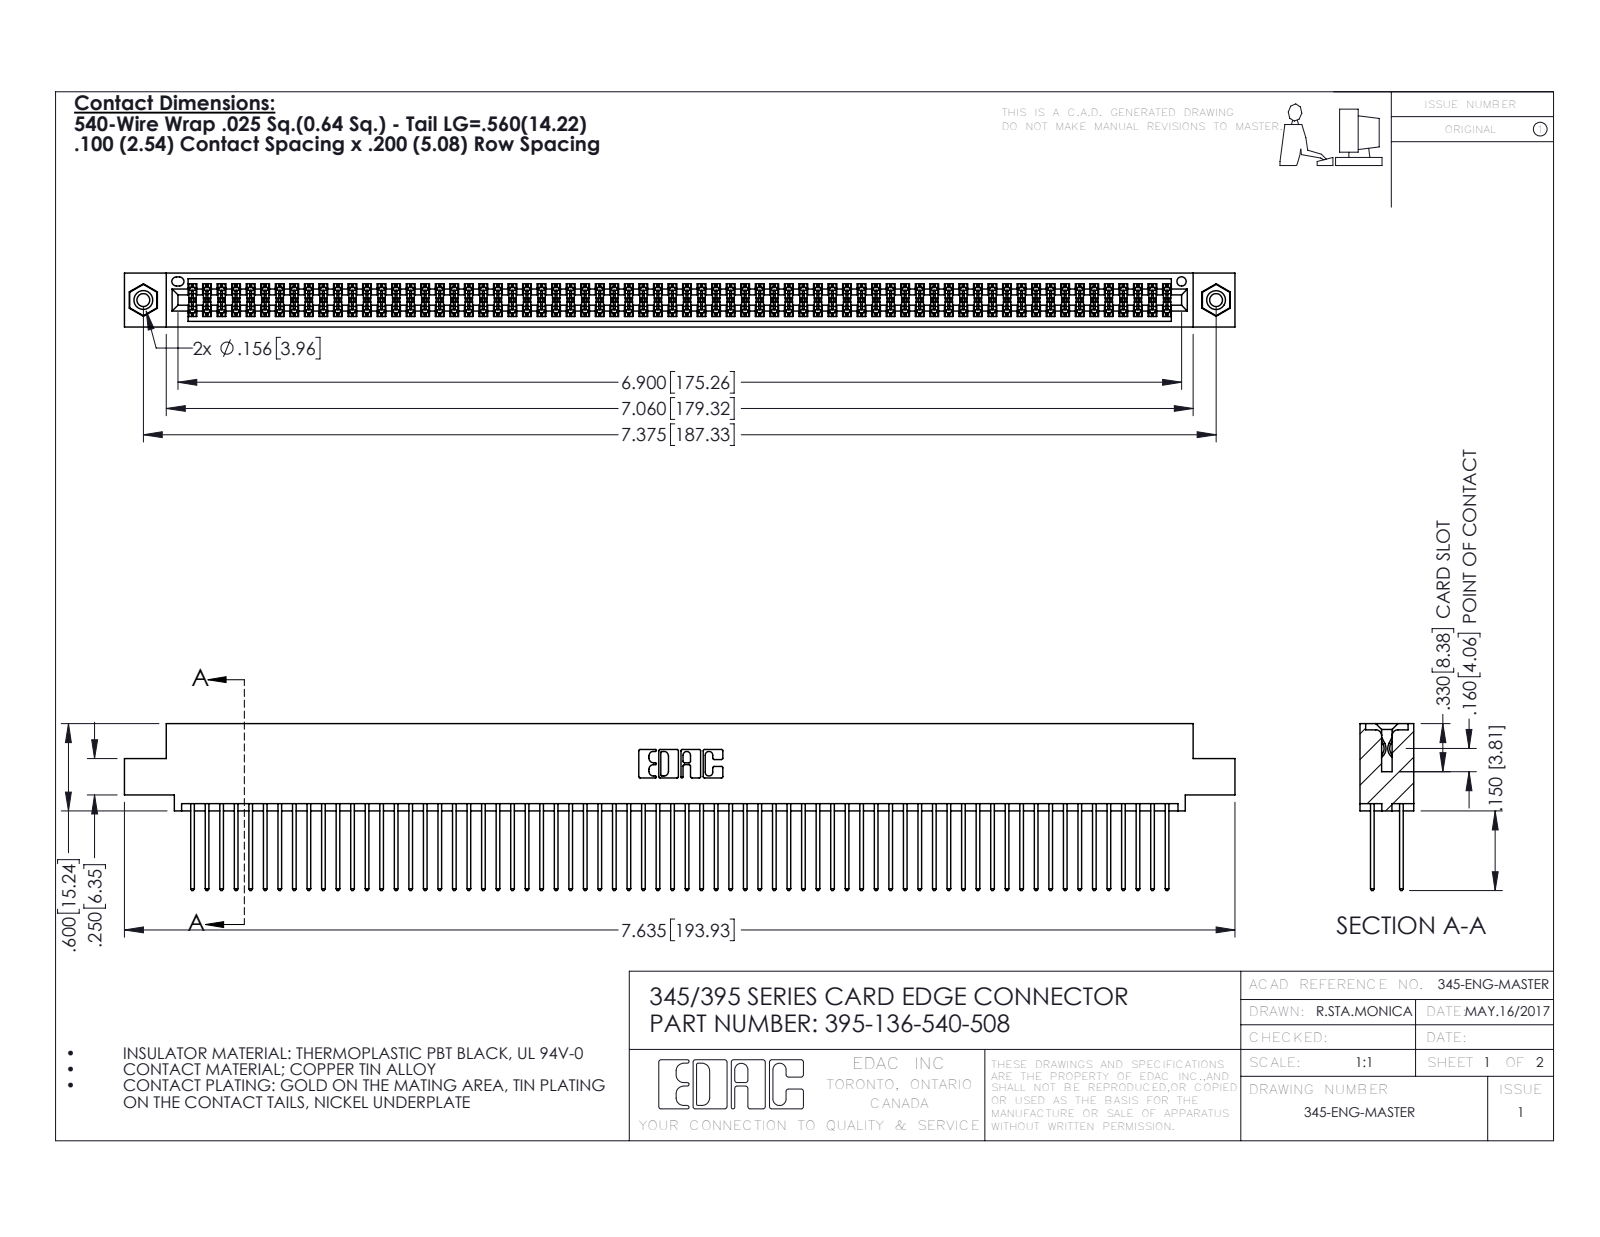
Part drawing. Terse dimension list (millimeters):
name: 345-292-001_345-293-140; 395-136-540-508; 345 Part_0.110 Offset - 0.156 Dia-TI; 345-250-001_345-250-003-102
written by: SolidWorks 2016 (CONFIG_CONTROL_DESIGN)
unit: mm
bodies: 139 solids, 6990 faces (4604 planar, 2370 cylindrical, 16 other)
size: 193.9 × 29.1 × 9.4
volume: 19 520 mm³; area: 31 850 mm²
holes: 2× ⌀2.3, 2× ⌀3.2, 2× ⌀4, 1× ⌀1.6
bosses: 2× ⌀3.9
rounds: 204× R0.2, 136× R0.3, 22× R0.3, 6× R0.2, 6× R0.8, 3× R0.7, 2× R0.4, 2× R0.5
face distances: 1.8, 7.6, 5.1, 2.5, 6.9, 0.6, 5.7, 9.4, 4.4, 3.8
hole spacings: 6.9, 181.3, 187.3
